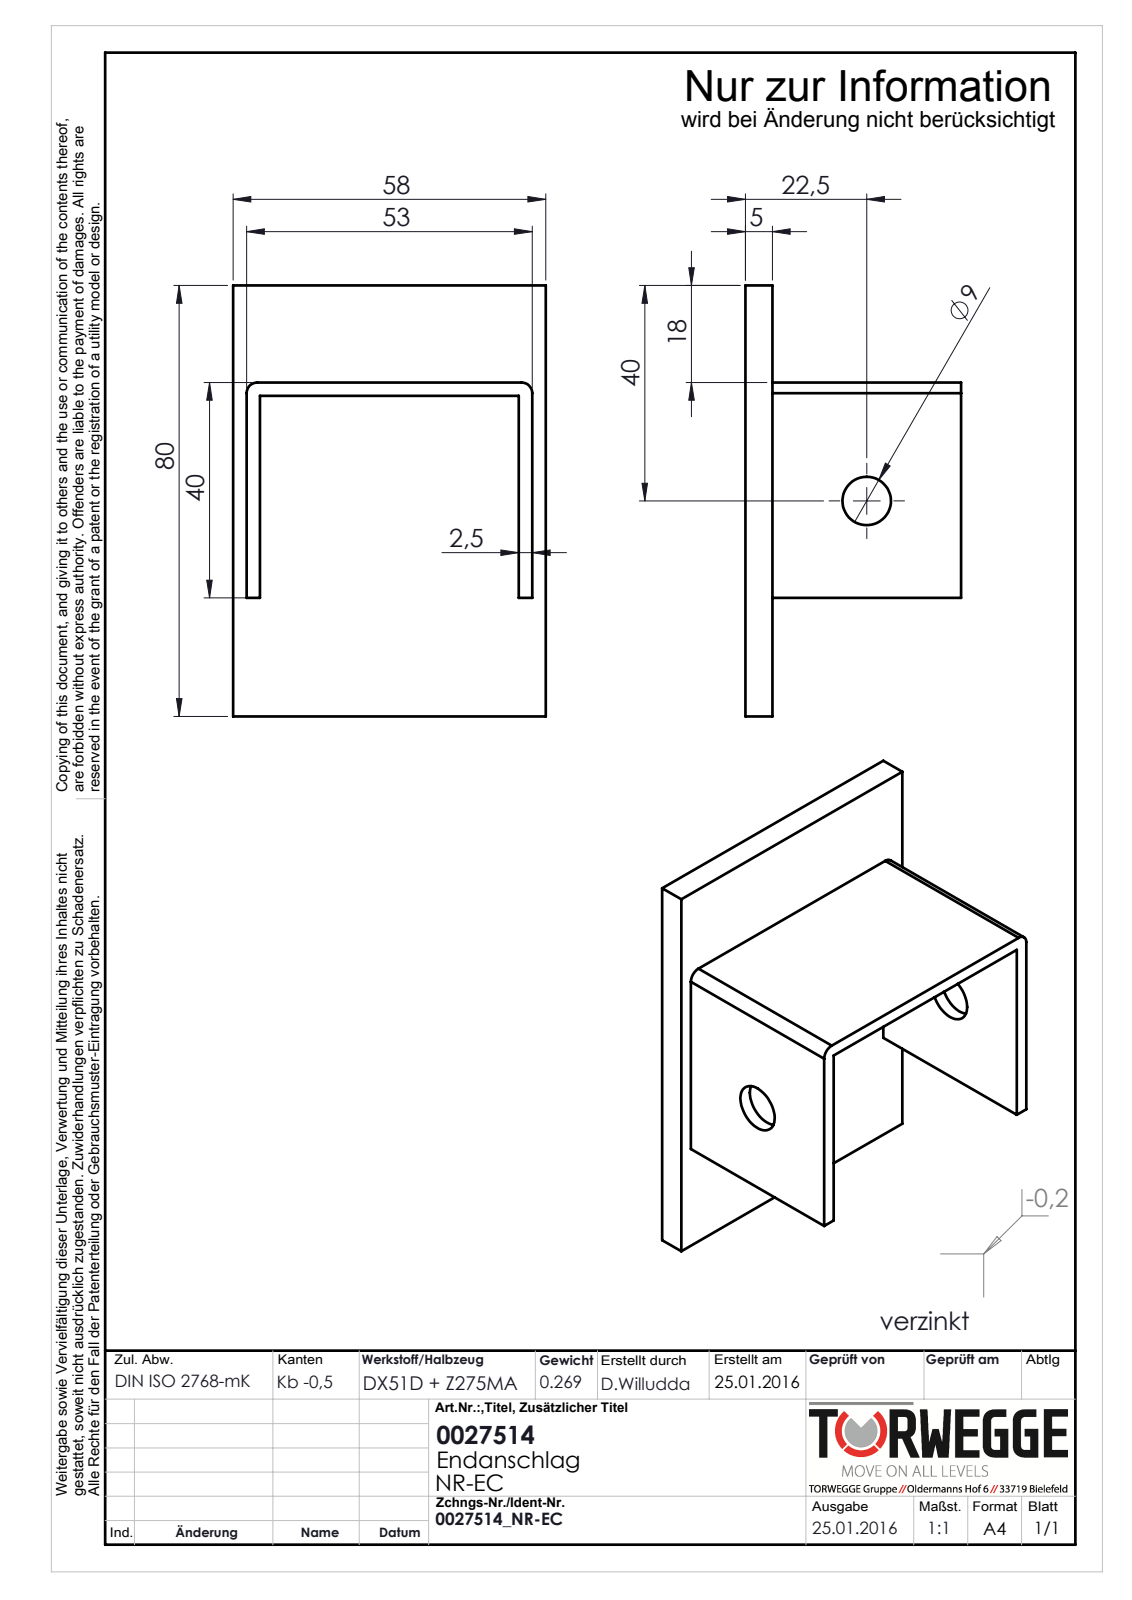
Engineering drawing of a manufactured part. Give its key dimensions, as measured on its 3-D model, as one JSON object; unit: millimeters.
{"part_name": "0027514_NR-EC", "step_written_by": "SolidWorks 2014 (AUTOMOTIVE_DESIGN)", "units": "millimeters", "bodies": {"solids": 1, "faces": 21, "planar": 15, "cylindrical": 6, "other": 0}, "overall_size": [80, 58, 40], "volume_mm3": 34022, "surface_area_mm2": 19622, "round_holes": [[9, 1]], "partial_cylinders_radius": [[2, 2]], "face_to_face_distances": [5, 2.5, 50.5, 53, 48, 55.5, 58, 40, 35, 59.5]}
